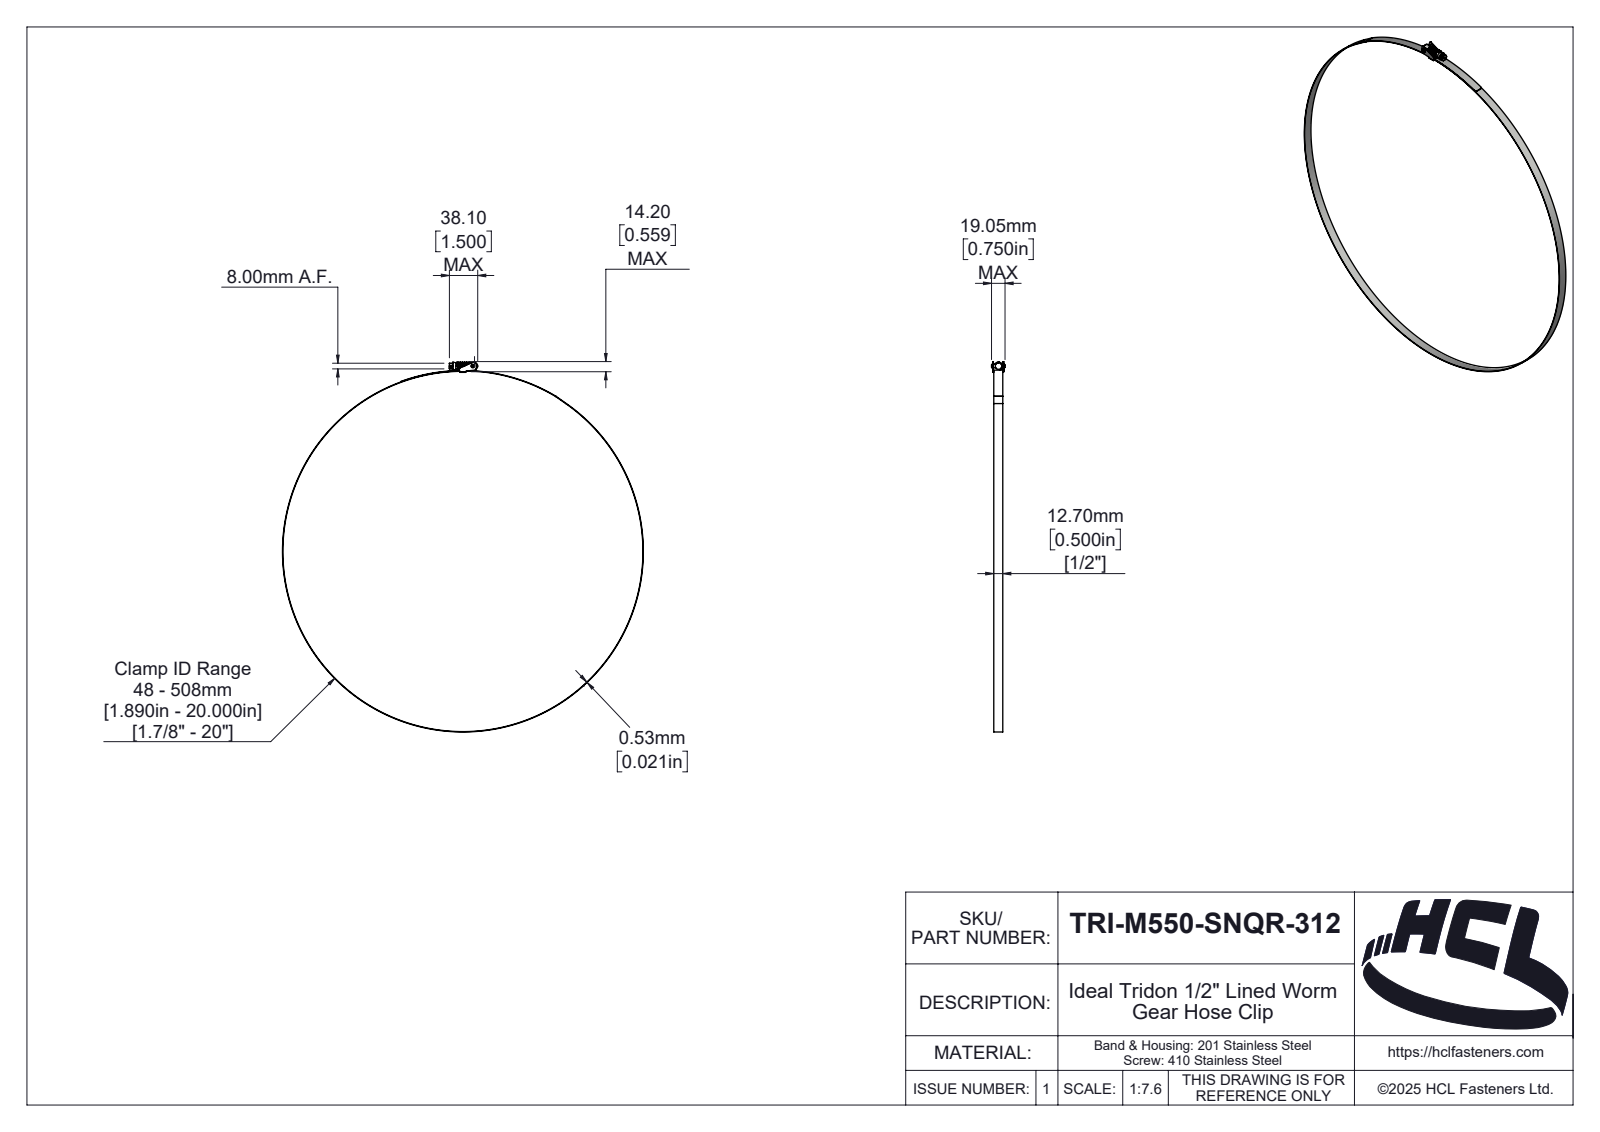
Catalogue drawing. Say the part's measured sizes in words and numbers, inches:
The part is named "TRI-M550-SNQR-312". Its 3-D file was written by "SolidWorks 2025 (AUTOMOTIVE_DESIGN)". It is 5 solids with 222 faces: 44 planar, 112 cylindrical and 66 other. Overall it measures 20.552 by 20.042 by 0.75 inches. Its volume is 0.887 cubic inches and its surface area 74.74 square inches. Round holes: 1 of diameter 0.197, 1 of diameter 20. Round bosses or shafts: 1 of diameter 20.042, 1 of diameter 0.358. Partial cylindrical surfaces (rounded edges, fillets, slot ends): 11 of radius 0.039, 2 of radius 0.004, 2 of radius 0.035, 2 of radius 0.118, 1 of radius 0.018, 1 of radius 0.074, 1 of radius 0.079, 1 of radius 0.093. The main face-to-face distances are 0.5, 0.031, 0.053, 0.553, 0.575, 0.022, 0.522, 0.021, 0.606, 0.543. The hole center spacings are 10.306.
